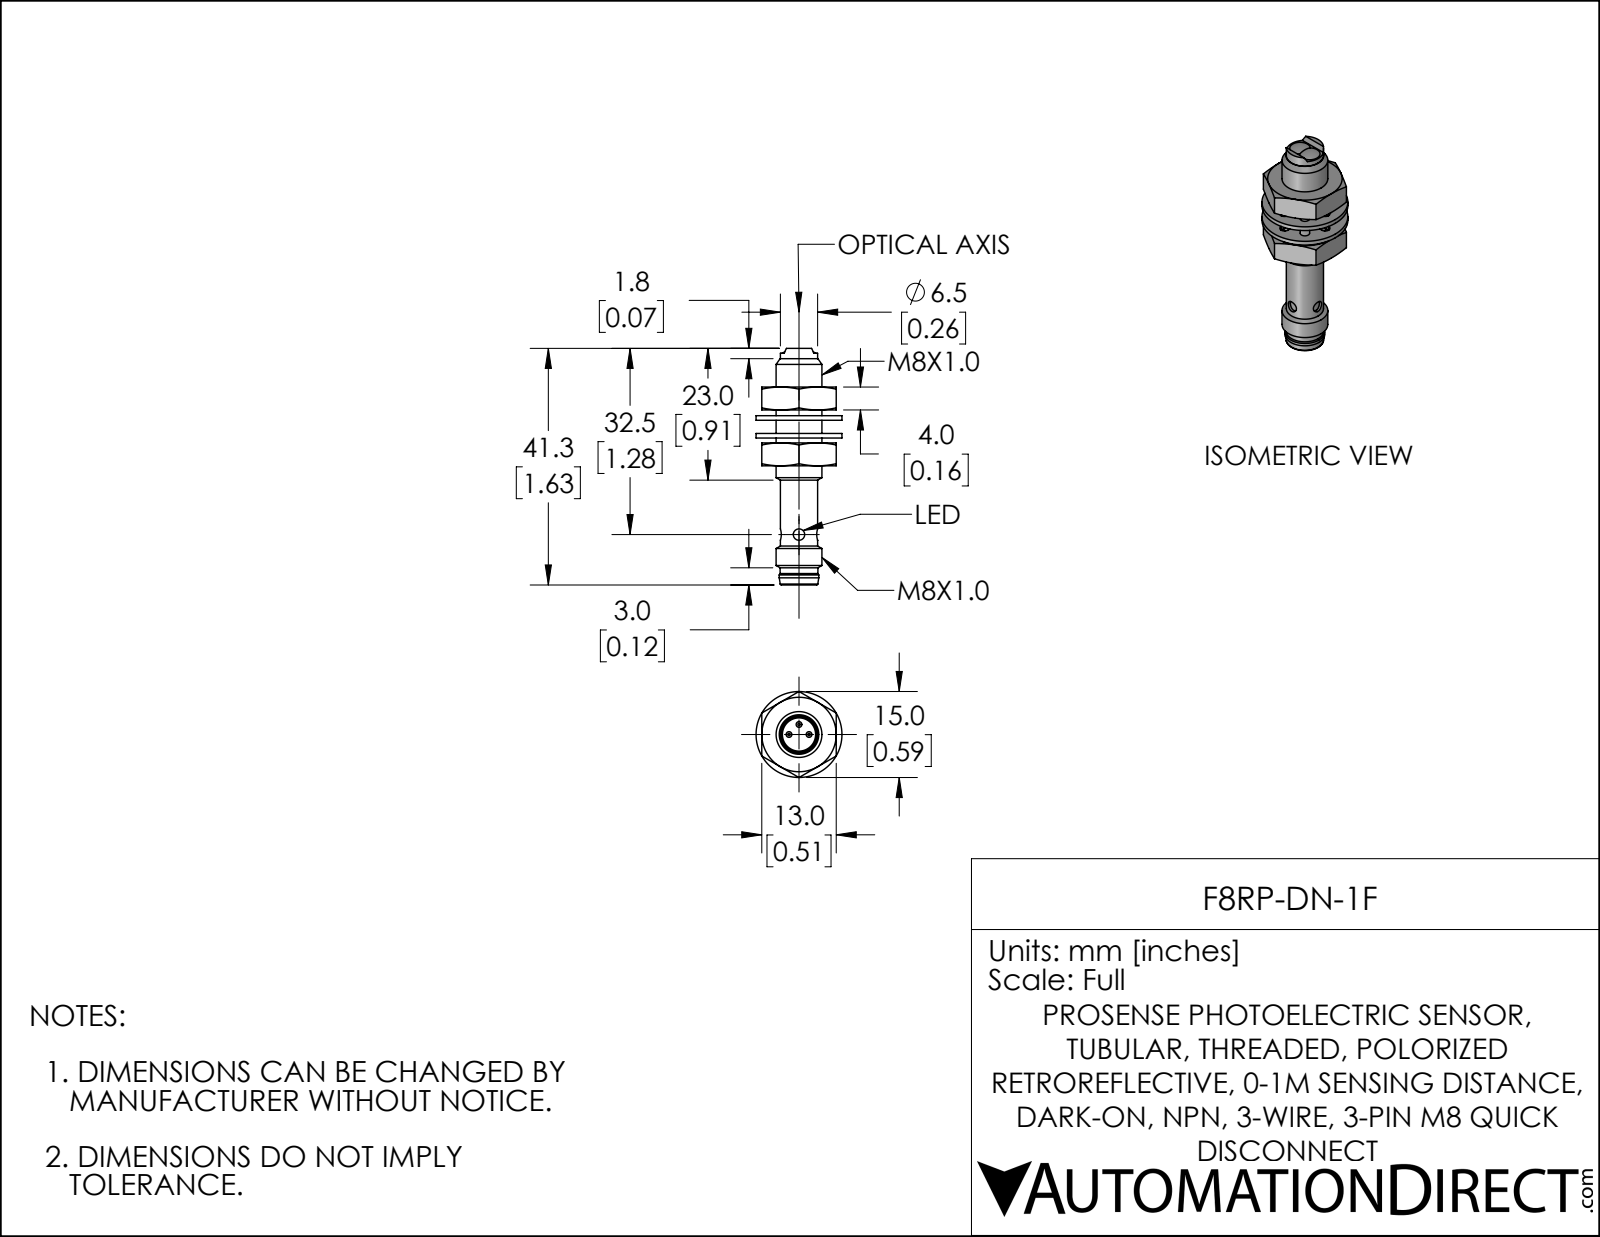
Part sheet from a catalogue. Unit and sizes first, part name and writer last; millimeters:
Units: millimetres
Overall size (bounding box): 41.3 × 15 × 15
Round holes (diameter × count): ⌀2 ×2, ⌀5.8 ×1, ⌀6.9 ×1
Round bosses / shafts (diameter × count): ⌀1 ×3, ⌀15 ×1, ⌀8 ×1, ⌀6.9 ×1, ⌀6.6 ×1, ⌀6.5 ×1
Partial cylindrical surfaces — rounded edges, fillets, slot ends (radius × count): R0.8 ×8, R2.8 ×1, R4.2 ×1
Main face-to-face distances: 3.1, 0.8, 13, 9.8, 4, 3.9, 2.3, 0.8, 1.7, 5
Volume: 2 650 mm³ · Surface area: 2 690 mm²
Bodies: 5 solids, 157 faces (63 planar, 54 cylindrical, 40 other)
Part name (STEP PRODUCT): F8RP-DN-1F
STEP written by: SolidWorks 2019 (CONFIG_CONTROL_DESIGN)
